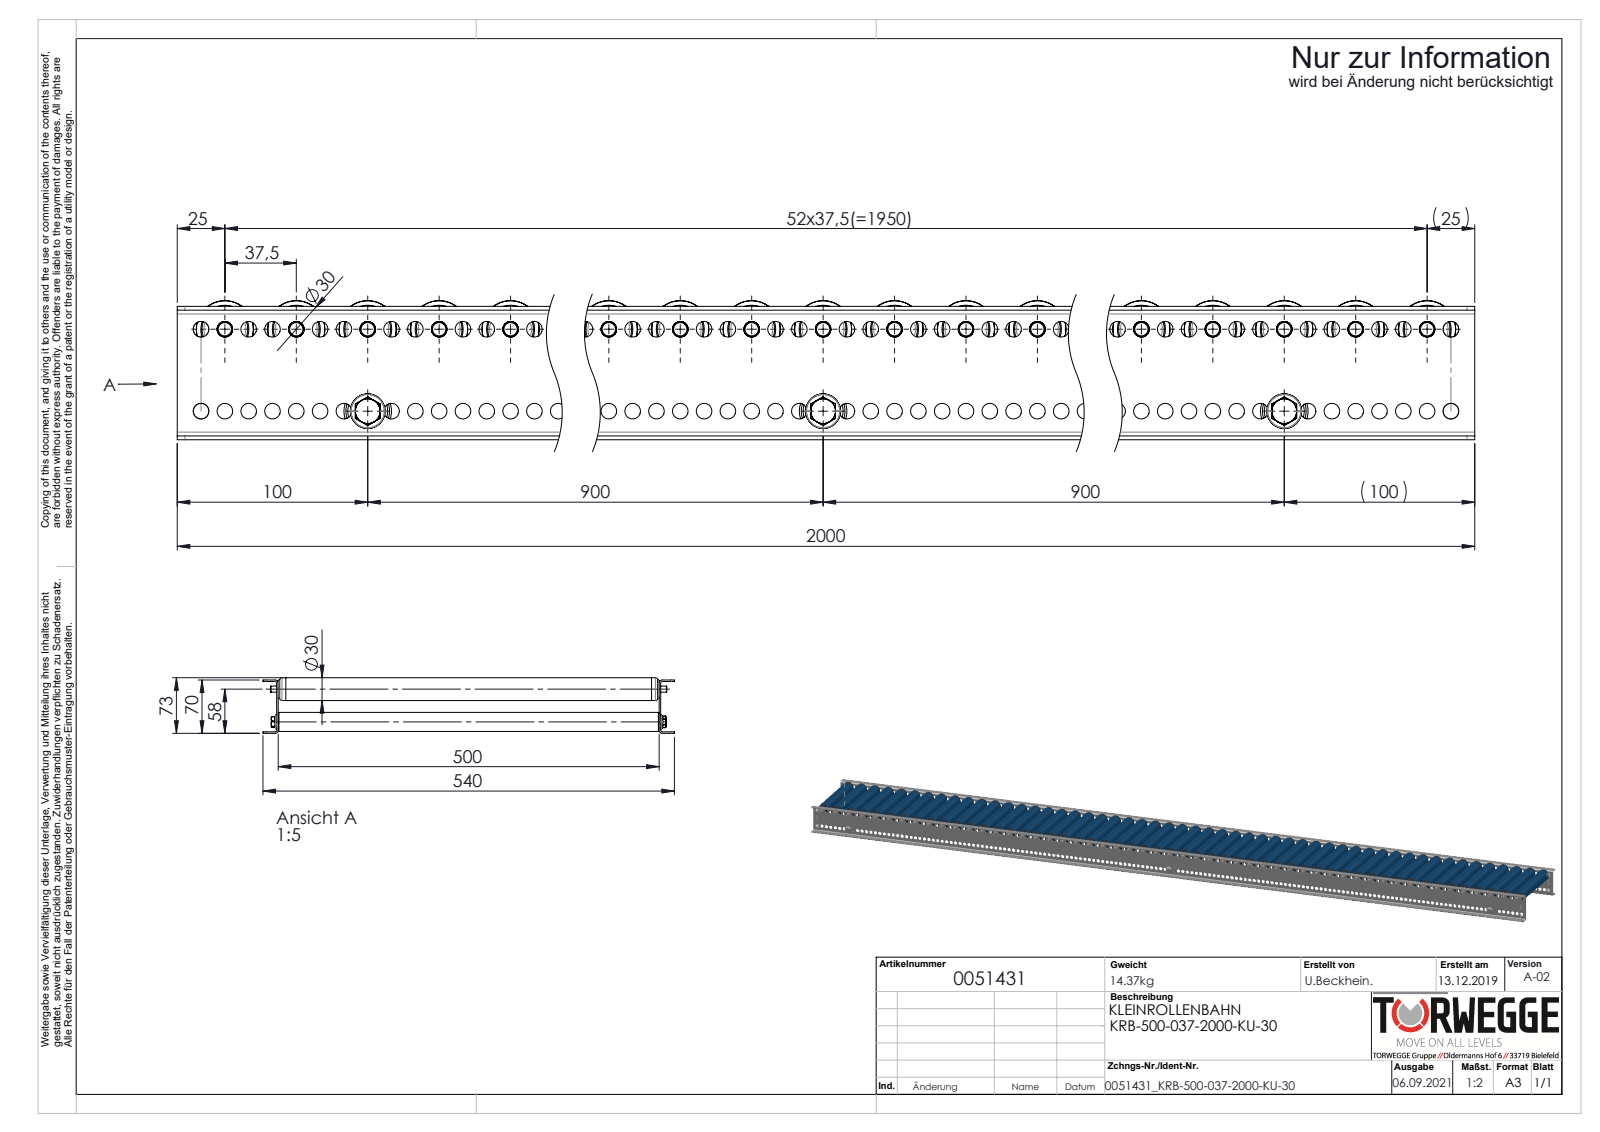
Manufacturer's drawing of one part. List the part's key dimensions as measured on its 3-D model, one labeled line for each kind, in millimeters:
Part name (STEP PRODUCT): KUT50-30x1,8-KB-A8-FA_KFG_0034507TWG_KUT50-30x1,8-KB-A8-FA-EL=500; Traversen_KFG_L500; S100994_Sperrzahnschraube_M08x16-8.8-A2K; 0017013_Tragrollenrohr-Ø30x1,8KU_KFG_L=480 (+4 more)
STEP written by: SolidWorks 2020 (AUTOMOTIVE_DESIGN)
Units: millimetres
Bodies: 123 solids, 12584 faces (3872 planar, 4740 cylindrical, 3972 other)
Overall size (bounding box): 2000 × 540 × 73
Volume: 6 460 000 mm³ · Surface area: 6 885 000 mm²
Round holes (diameter × count): ⌀8.2 ×318, ⌀8.1 ×53, ⌀22.6 ×53, ⌀25.2 ×53, ⌀6.8 ×3, ⌀21 ×3
Round bosses / shafts (diameter × count): ⌀8 ×56, ⌀30 ×53, ⌀29.9 ×53, ⌀26.5 ×53, ⌀26.4 ×53, ⌀24 ×53, ⌀25 ×3
Partial cylindrical surfaces — rounded edges, fillets, slot ends (radius × count): R5.05 ×53, R4 ×8, R2 ×4
Main face-to-face distances: 2, 502, 500, 68, 504, 70, 66, 10, 490, 12
Hole centre spacings: 12.5, 25, 37.5, 50, 62.5, 75, 87.5, 100
